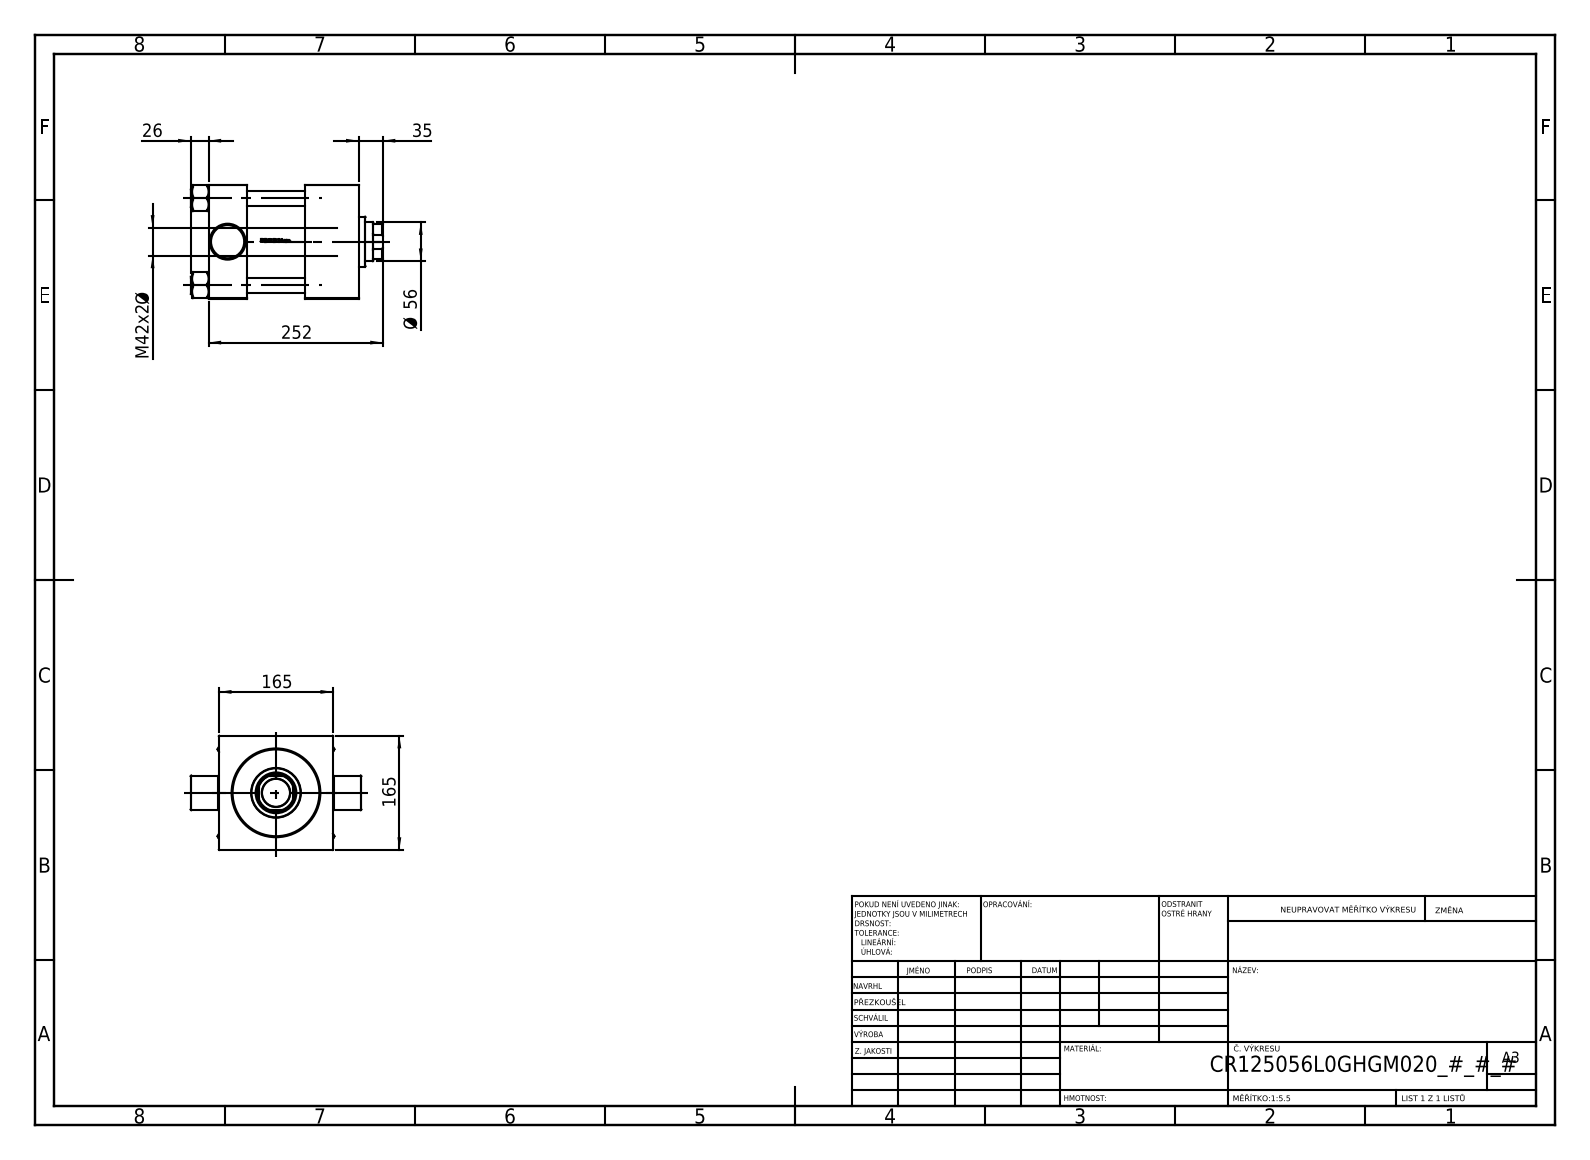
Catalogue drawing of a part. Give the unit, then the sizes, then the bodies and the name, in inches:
Units: inches
Overall size (bounding box): 10.945 × 9.724 × 6.496
Round holes (diameter × count): ⌀0.866 ×4, ⌀0.276 ×1, ⌀1.594 ×1, ⌀2.205 ×1, ⌀2.323 ×1, ⌀3.78 ×1, ⌀4.921 ×1, ⌀4.941 ×1
Round bosses / shafts (diameter × count): ⌀0.984 ×4, ⌀5.157 ×1, ⌀2.835 ×1, ⌀1.969 ×1
Partial cylindrical surfaces — rounded edges, fillets, slot ends (radius × count): R1.063 ×1
Main face-to-face distances: 6.496, 2.165, 8.543, 6.378, 5.472, 3.307, 3.071, 2.52, 3.858, 4.685
Hole centre spacings: 3.505, 4.957, 7.01
Volume: 288.2 in³ · Surface area: 777.5 in²
Bodies: 11 solids, 1105 faces (473 planar, 110 cylindrical, 522 other)
Part name (STEP PRODUCT): V215CR_L_Body; V215CR_L_TYCINKA; V215CR_VCP_L; NUT_M5_L (+1 more)
STEP written by: SolidWorks 2019 (CONFIG_CONTROL_DESIGN)
